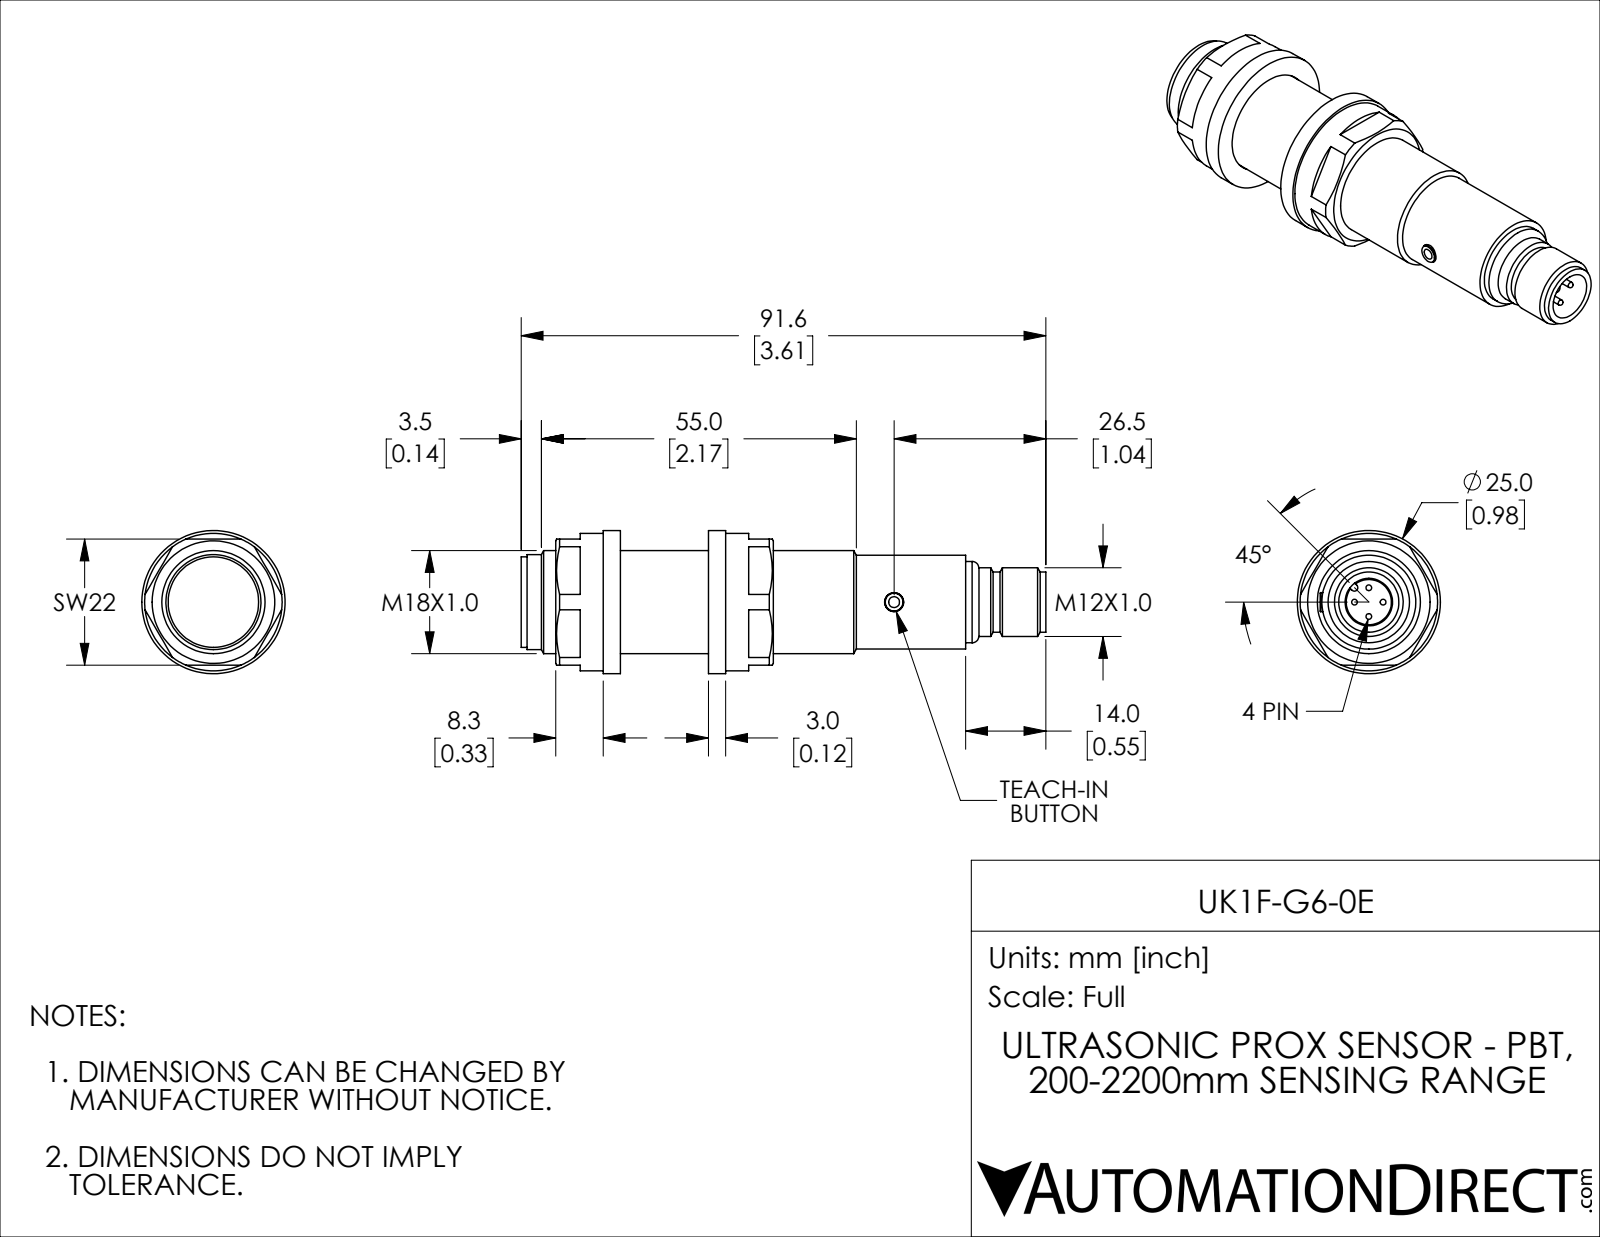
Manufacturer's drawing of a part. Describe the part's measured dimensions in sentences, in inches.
The part is named "UK1F-G6-0E". Its 3-D file was written by "SolidWorks 2018 (AUTOMOTIVE_DESIGN)". It is 6 solids with 123 faces: 43 planar, 49 cylindrical and 31 other. Overall it measures 3.606 by 0.984 by 0.984 inches. Its volume is 1.477 cubic inches and its surface area 16.01 square inches. Round holes: 1 of diameter 0.13, 1 of diameter 0.327, 1 of diameter 0.709, 1 of diameter 0.717. Round bosses or shafts: 4 of diameter 0.039, 1 of diameter 0.984, 1 of diameter 0.945, 1 of diameter 0.654, 1 of diameter 0.646, 1 of diameter 0.622, 1 of diameter 0.559, 1 of diameter 0.472. Partial cylindrical surfaces (rounded edges, fillets, slot ends): 1 of radius 0.024. The main face-to-face distances are 0.118, 0.724, 0.843, 0.606, 0.866, 0.327, 0.445, 1.051, 1.169, 0.563.
